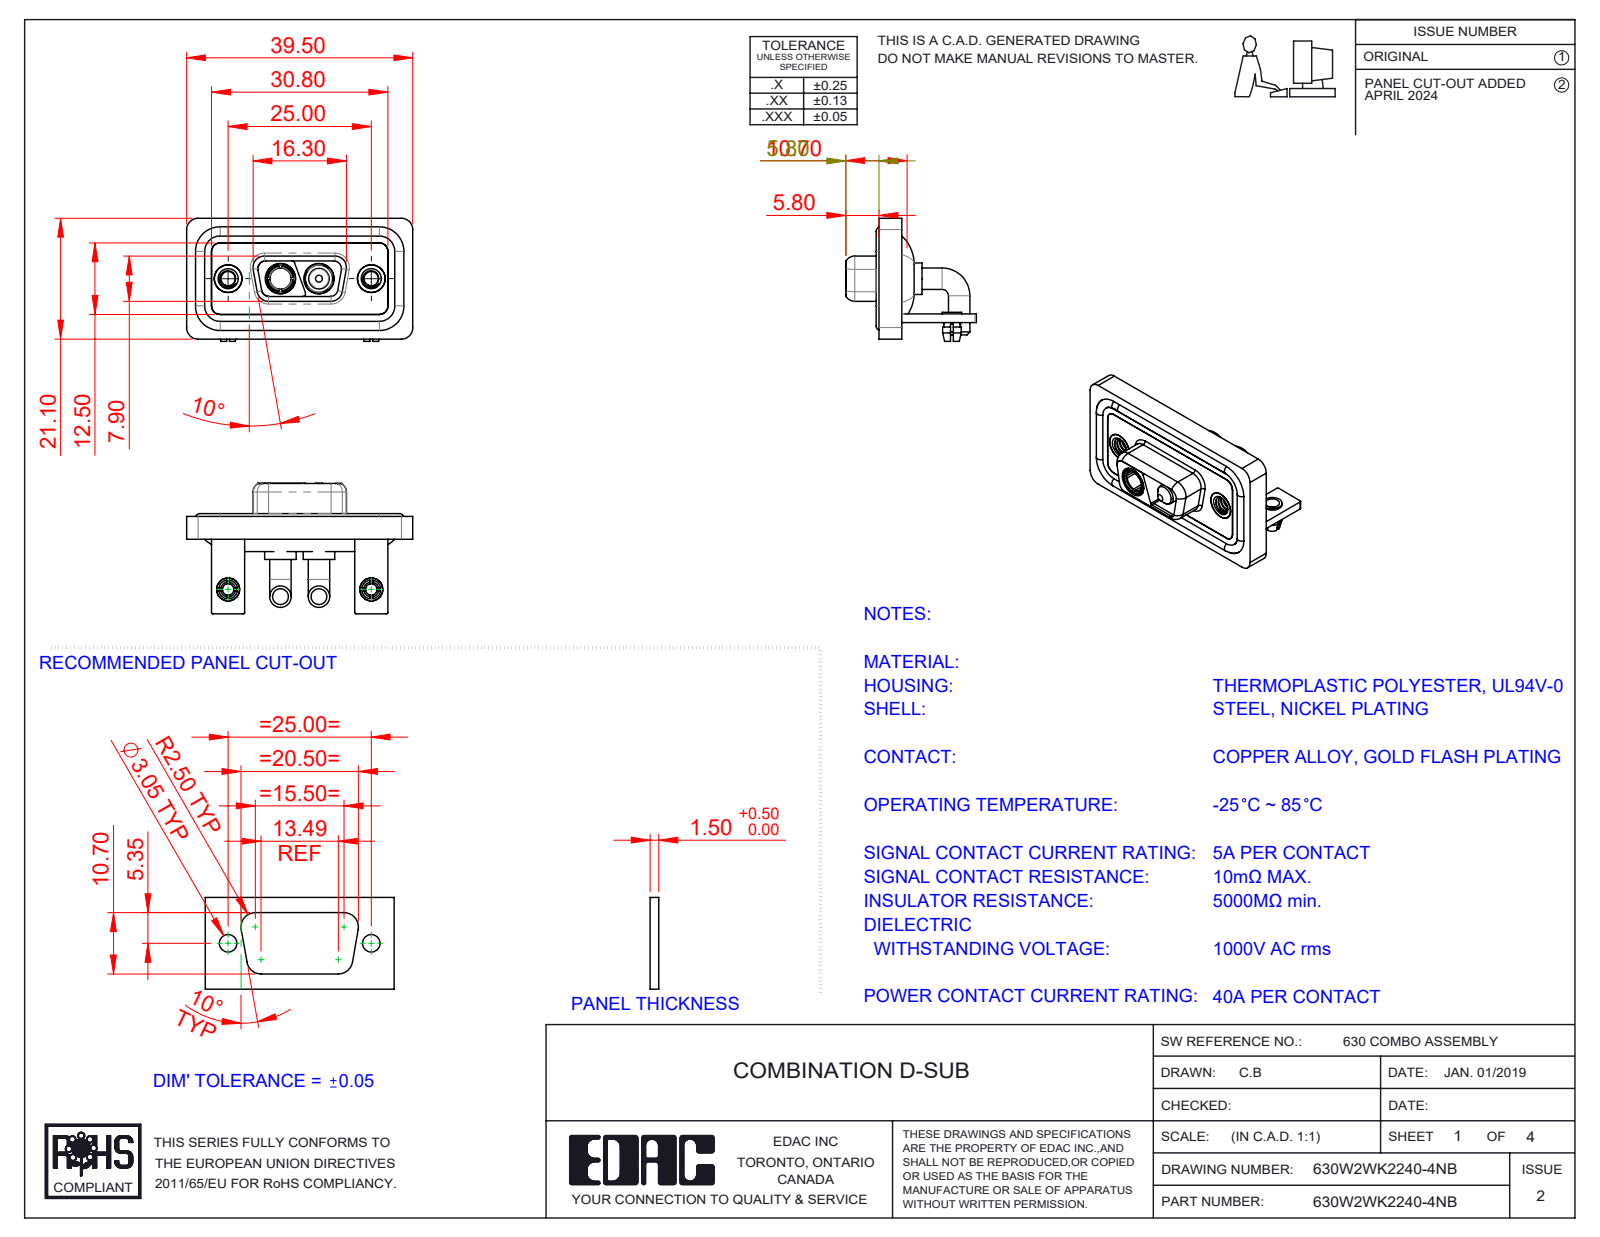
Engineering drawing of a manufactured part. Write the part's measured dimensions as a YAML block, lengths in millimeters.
part_name: "630Combo Threaded Rivet_A; 630Combo Board Lock_50 Contacts; 630Combo Shell Front_09 Contacts; Power Socket_40A RA (+6 more)"
step_written_by: "SolidWorks 2023 (CONFIG_CONTROL_DESIGN)"
units: millimeters
bodies: {solids: 15, faces: 642, planar: 212, cylindrical: 289, other: 141}
overall_size: [39.5, 22.8, 21.5]
volume: 5248
surface_area: 8531
round_holes:
  - {diameter: 2.5, count: 4}
  - {diameter: 4.85, count: 4}
  - {diameter: 2, count: 2}
  - {diameter: 3.2, count: 2}
  - {diameter: 4, count: 2}
  - {diameter: 4.05, count: 2}
  - {diameter: 5, count: 2}
  - {diameter: 5.3, count: 2}
  - {diameter: 3.7, count: 1}
round_bosses_or_shafts:
  - {diameter: 3.75, count: 4}
  - {diameter: 1.6, count: 4}
  - {diameter: 5.5, count: 2}
  - {diameter: 5.2, count: 2}
  - {diameter: 4.95, count: 2}
  - {diameter: 4.8, count: 2}
  - {diameter: 4.75, count: 2}
  - {diameter: 4, count: 2}
partial_cylinders:
  - {radius: 2, count: 19}
  - {radius: 1.5, count: 18}
  - {radius: 0.25, count: 16}
  - {radius: 1.35, count: 8}
  - {radius: 1.6, count: 8}
  - {radius: 0.5, count: 7}
  - {radius: 0.6, count: 4}
  - {radius: 0.65, count: 4}
face_to_face_distances: [0.4, 2.9, 1.5, 1.1, 3.7, 1.8, 0.8, 2.5, 1.6, 3.1]
hole_center_spacings: [9.14, 15.86, 25, 6.72]
